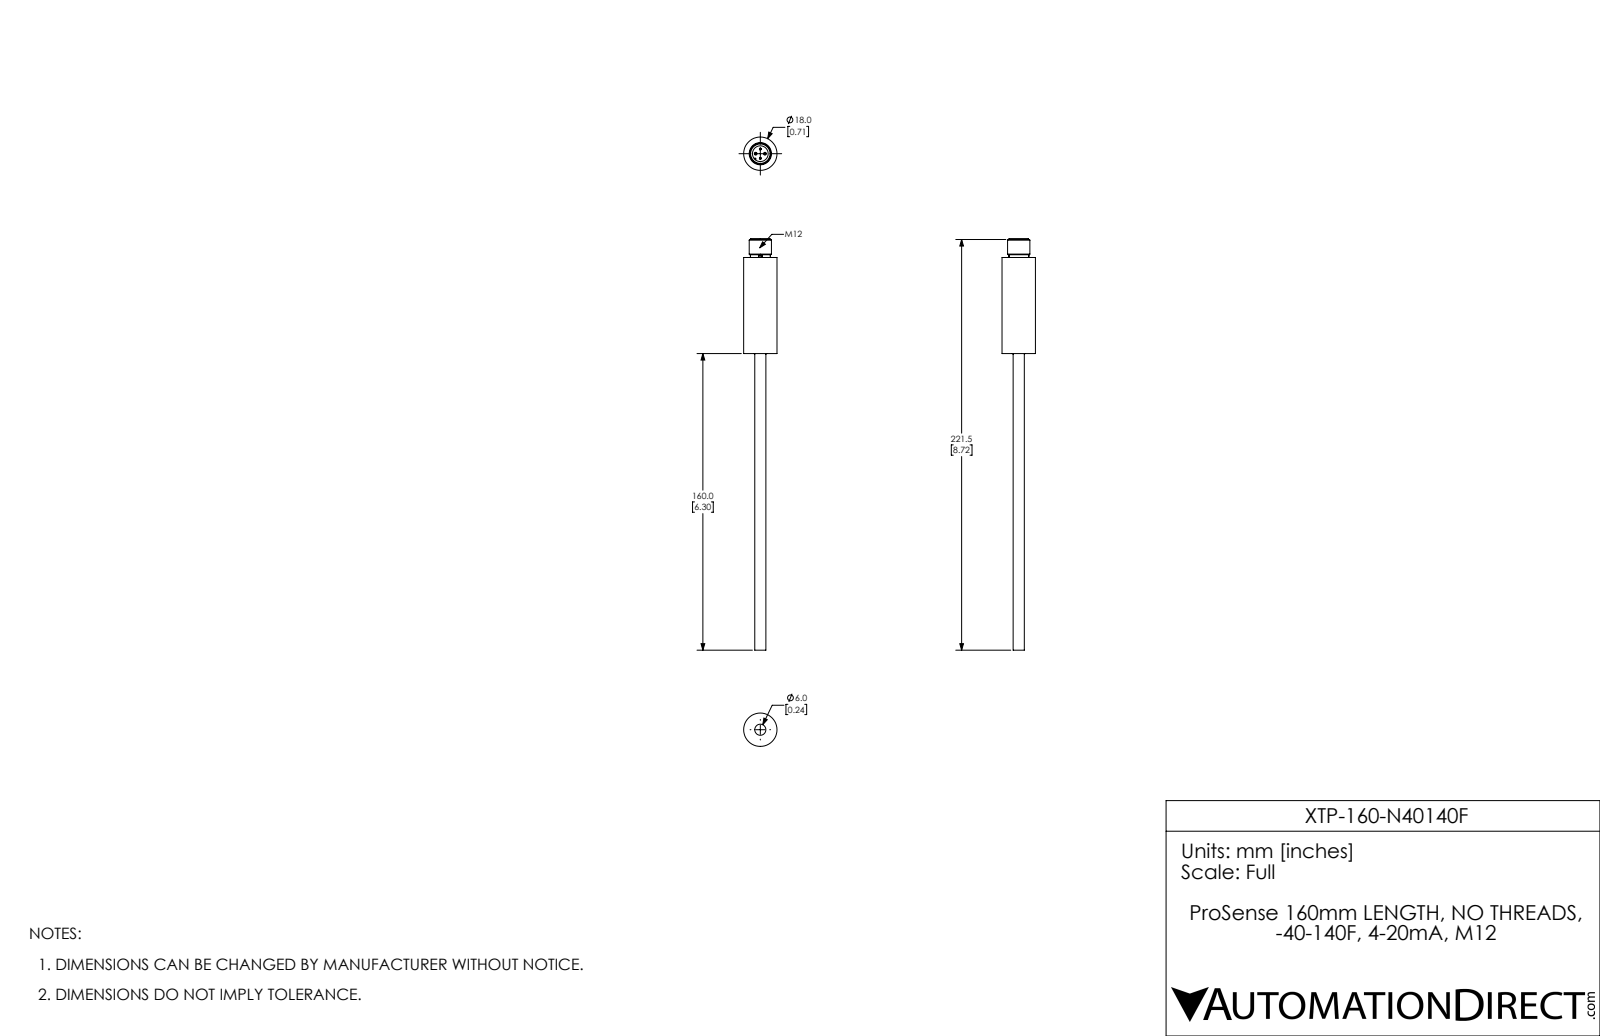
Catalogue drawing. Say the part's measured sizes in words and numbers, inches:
The part is named "XTP-160-N40140F". Its 3-D file was written by "SolidWorks 2017 (AUTOMOTIVE_DESIGN)". It is 1 solid with 67 faces: 24 planar, 21 cylindrical and 22 other. Overall it measures 8.74 by 0.709 by 0.709 inches. Its volume is 1.118 cubic inches and its surface area 11.09 square inches. Round holes: 1 of diameter 0.335. Round bosses or shafts: 4 of diameter 0.04, 1 of diameter 0.709, 1 of diameter 0.472, 1 of diameter 0.421, 1 of diameter 0.413, 1 of diameter 0.236. Partial cylindrical surfaces (rounded edges, fillets, slot ends): 1 of radius 0.016. The main face-to-face distances are 2.039, 2.087, 0.047, 2.441, 0.402, 0.354, 6.299, 8.339, 8.386, 8.74.
